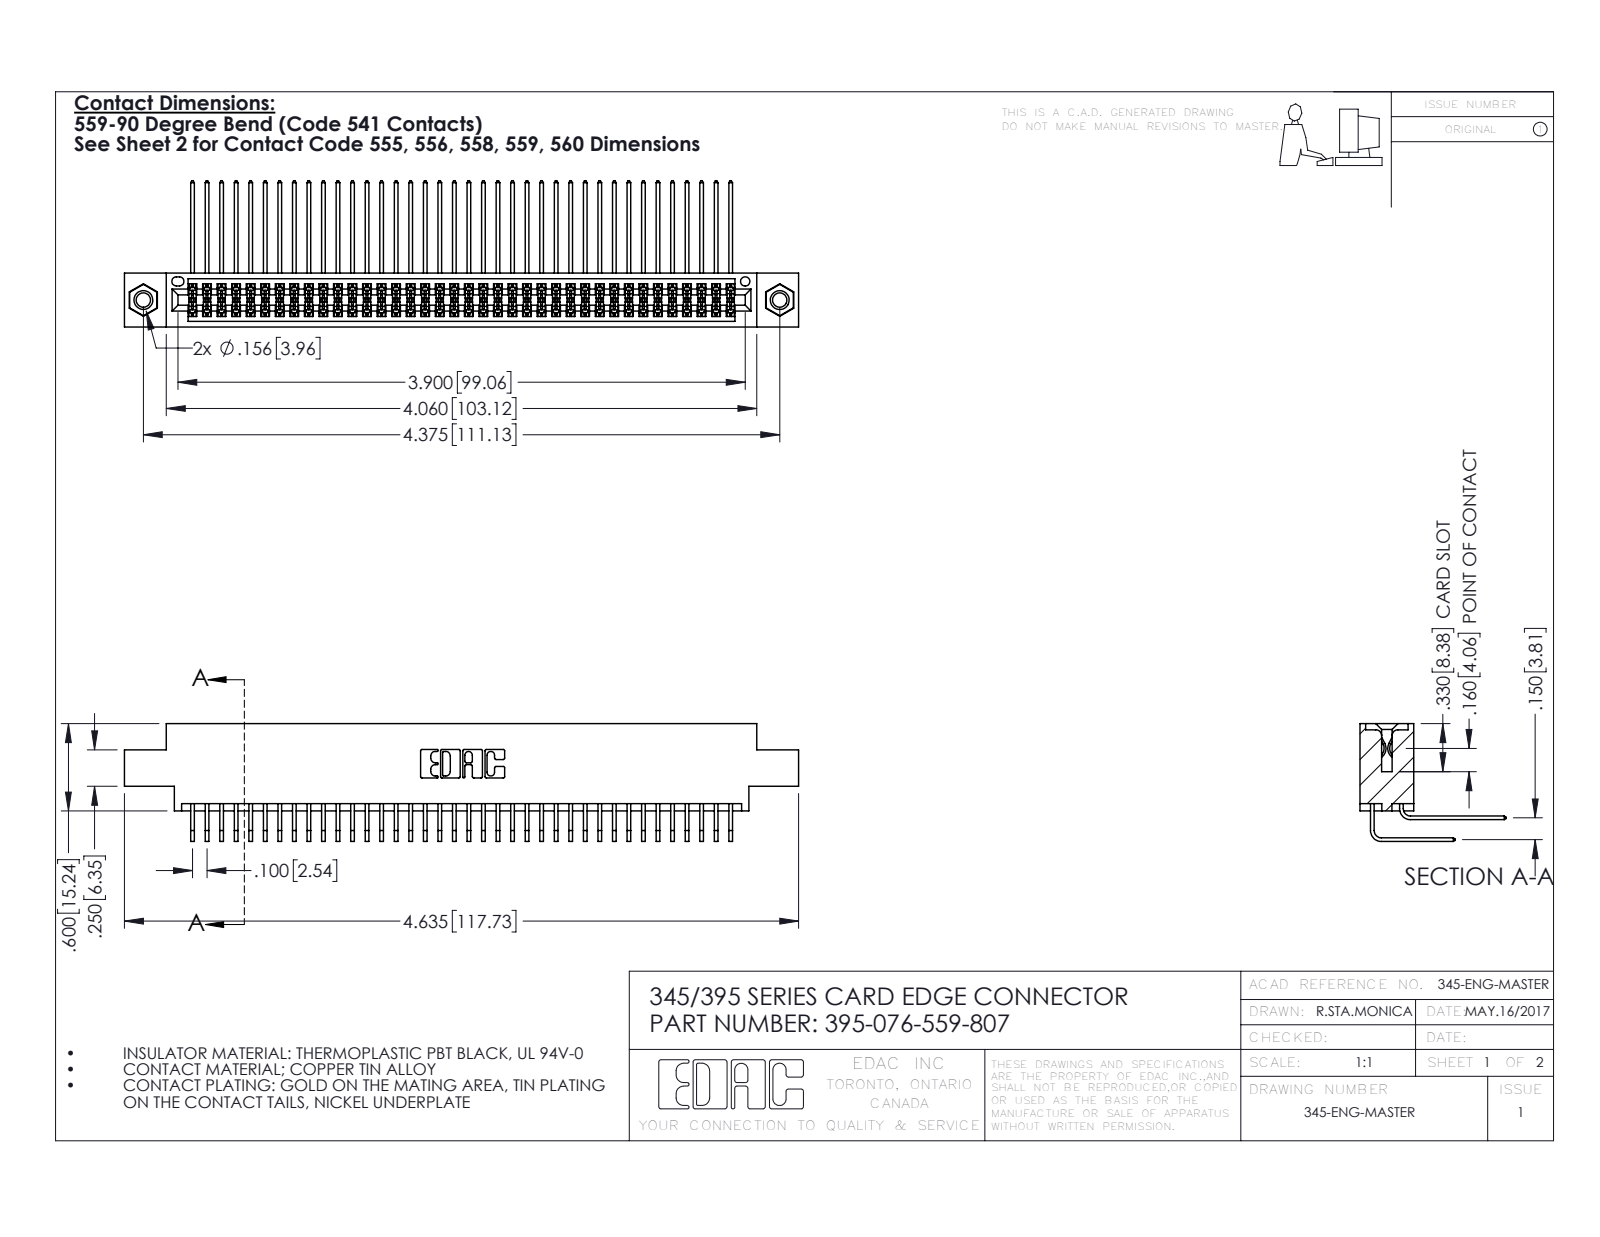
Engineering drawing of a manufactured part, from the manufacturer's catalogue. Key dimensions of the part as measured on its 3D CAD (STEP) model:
Part name (STEP PRODUCT): 395-076-559-807; 345-292-001_559 Tail - 2; 345-292-001_558 559 Tail - 1; 345-250-001_345-250-005-103 (+1 more)
STEP written by: SolidWorks 2016 (CONFIG_CONTROL_DESIGN)
Units: inches
Bodies: 79 solids, 4142 faces (2776 planar, 1350 cylindrical, 16 other)
Overall size (bounding box): 4.635 × 1.005 × 0.809
Volume: 0.715 in³ · Surface area: 30.17 in²
Round holes (diameter × count): ⌀0.098 ×2, ⌀0.125 ×2, ⌀0.156 ×2, ⌀0.064 ×1
Round bosses / shafts (diameter × count): ⌀0.155 ×2
Partial cylindrical surfaces — rounded edges, fillets, slot ends (radius × count): R0.006 ×114, R0.01 ×22, R0.007 ×6, R0.031 ×6, R0.026 ×3, R0.014 ×2, R0.019 ×2, R0.022 ×2
Main face-to-face distances: 0.072, 0.298, 0.37, 0.2, 0.098, 0.272, 0.025, 0.225, 0.175, 0.15
Hole centre spacings: 0.27, 4.139, 4.375
